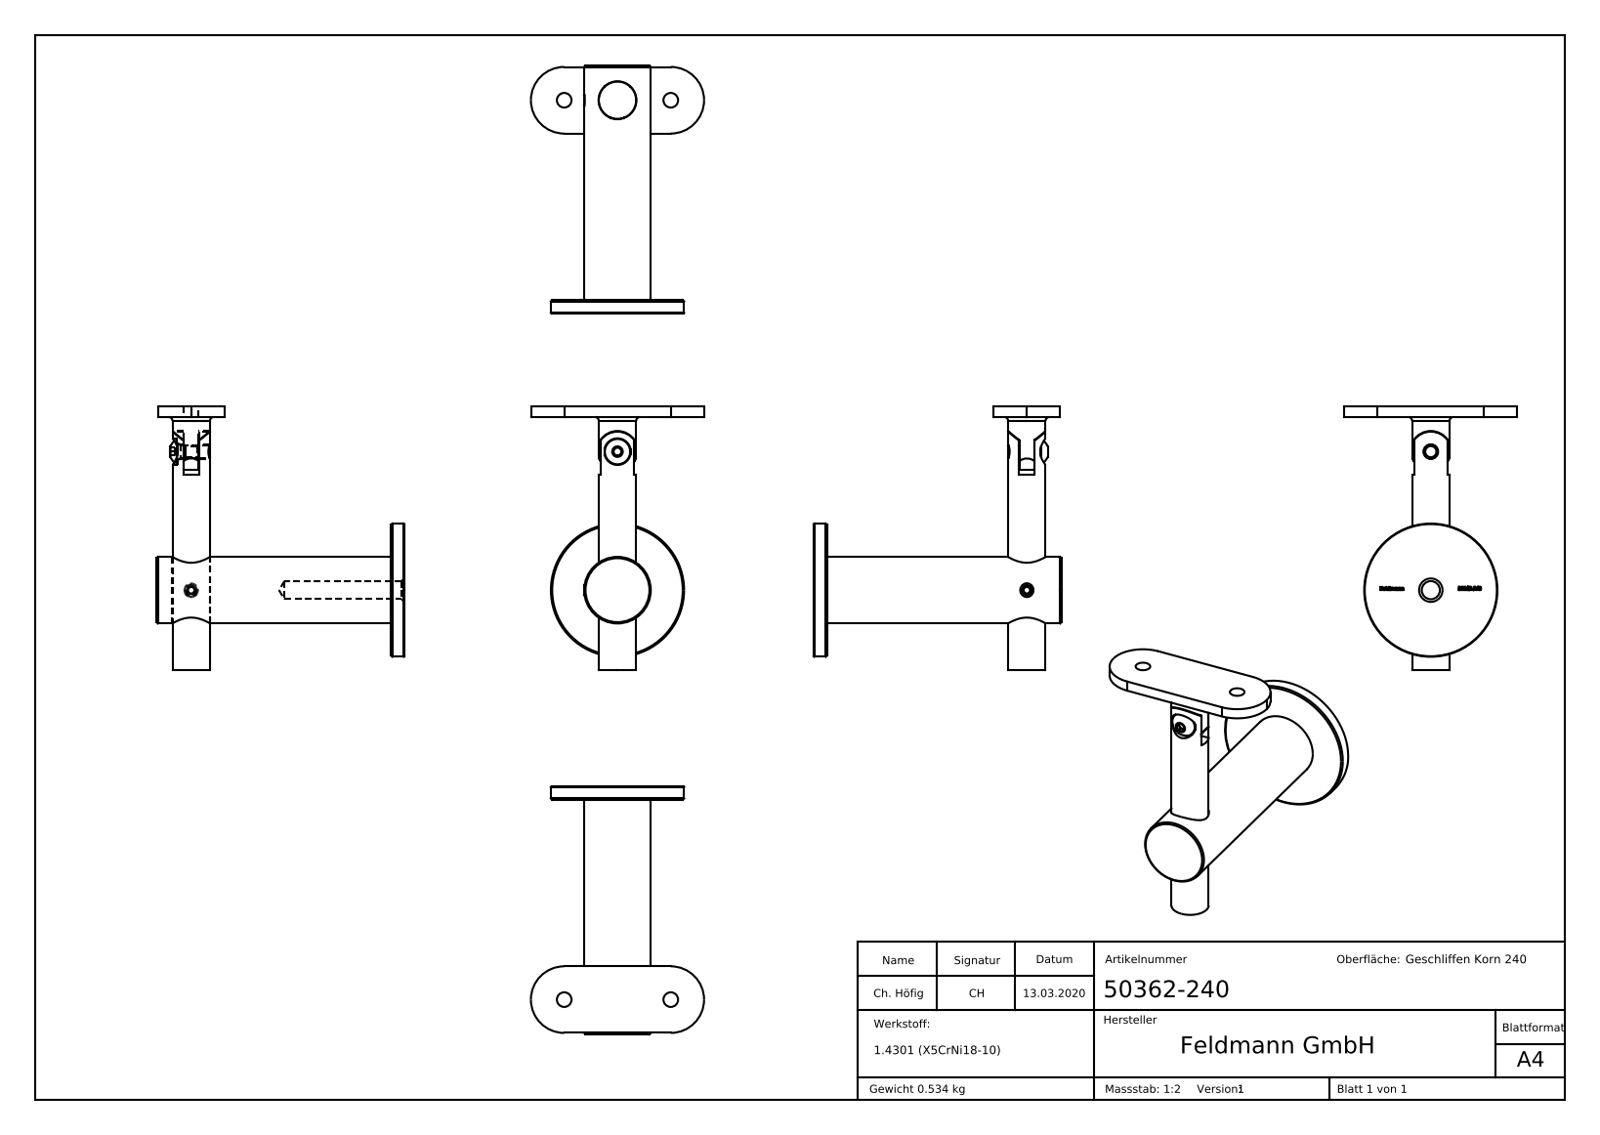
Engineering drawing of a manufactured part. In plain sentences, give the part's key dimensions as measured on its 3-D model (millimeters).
The part is named "50362-240; 503XX-240 Teil1; 503XX-240 Teil4; 503XX-240 Teil3 (+7 more)". Its 3-D file was written by "SolidWorks 2015 (CONFIG_CONTROL_DESIGN)". It is 5 solids with 314 faces: 157 planar, 26 cylindrical and 131 other. Overall it measures 99 by 93 by 88 millimeters. Its volume is 67 629 cubic millimeters and its surface area 22 568 square millimeters. Round holes: 3 of diameter 5.5, 2 of diameter 4.2, 1 of diameter 6.8, 1 of diameter 10, 1 of diameter 14.2. Round bosses or shafts: 2 of diameter 5, 1 of diameter 50, 1 of diameter 25, 1 of diameter 14, 1 of diameter 9.5. Partial cylindrical surfaces (rounded edges, fillets, slot ends): 3 of radius 7.75, 2 of radius 12.5. The main face-to-face distances are 5, 4, 93, 88, 15.5, 9.5, 9.75, 15.25, 5.75, 25.5. The hole center spacings are 20, 40, 52.
